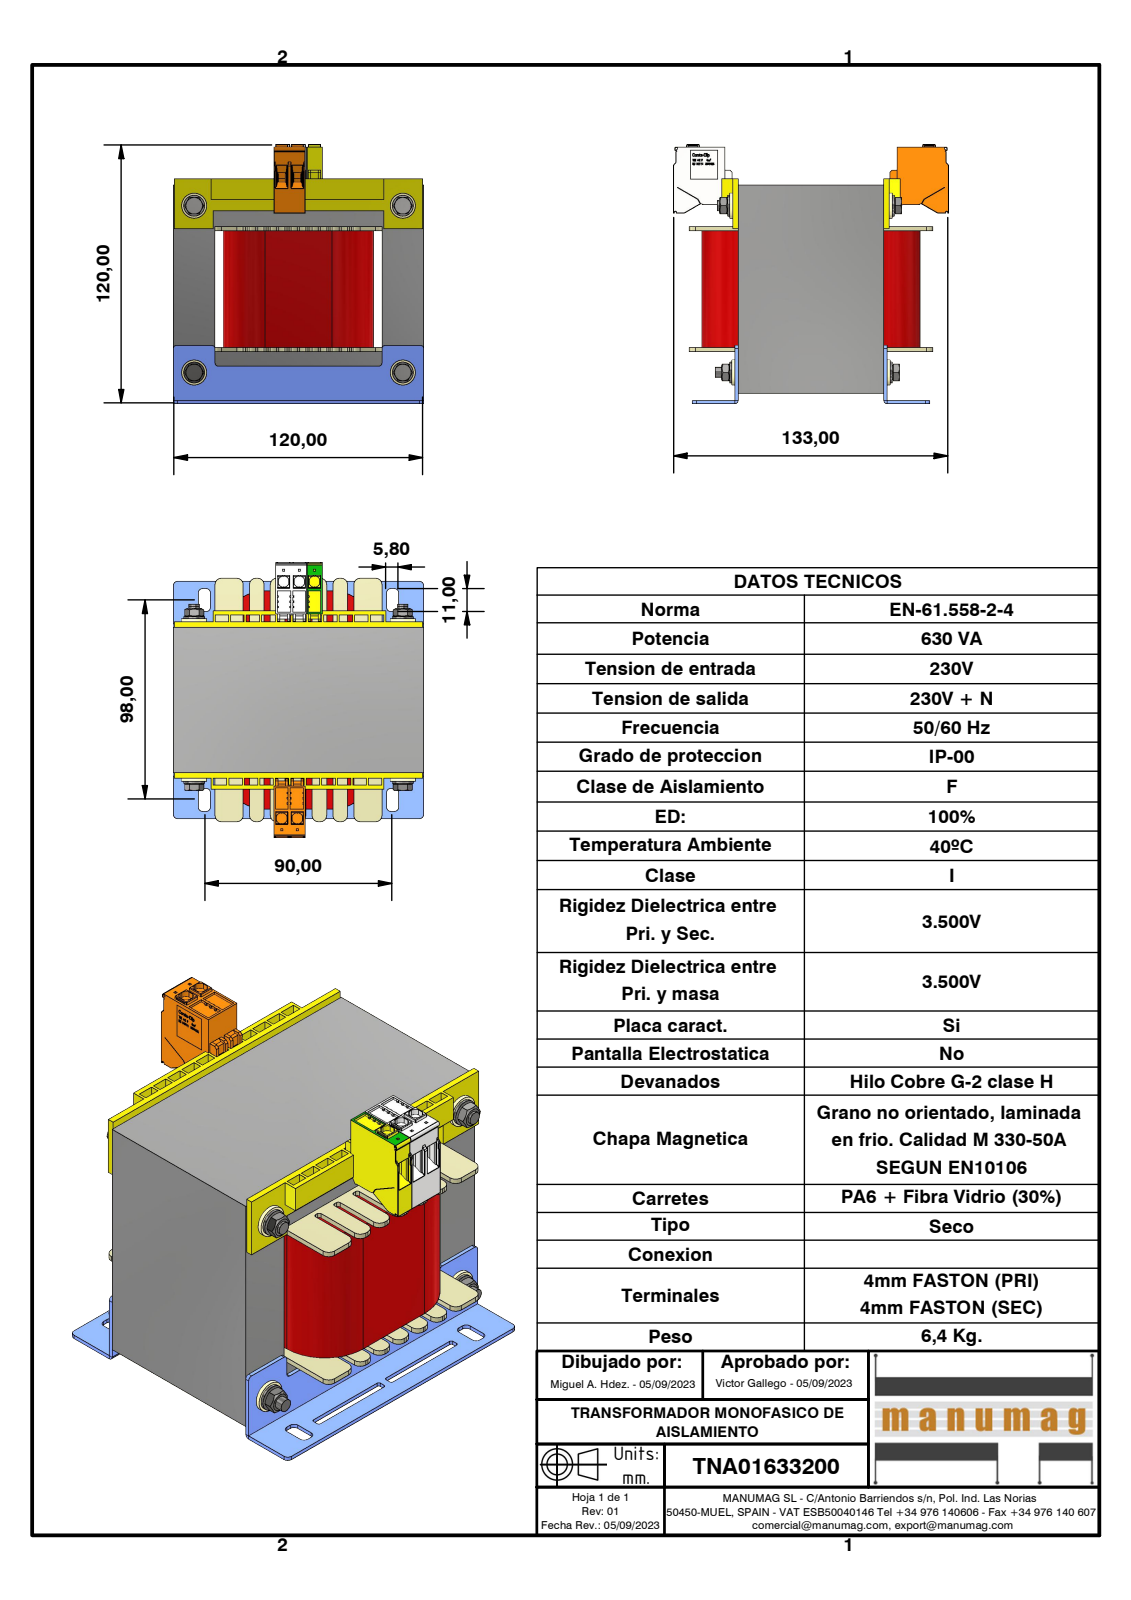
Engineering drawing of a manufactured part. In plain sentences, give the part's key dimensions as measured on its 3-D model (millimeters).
The part is named "TNA01633200; EI120 x 100 - 70 (Rc40); AF40DIN; EI 120 X 100 - 70 (+8 more)". Its 3-D file was written by "Autodesk Inventor 2023 (AUTOMOTIVE_DESIGN)". It is 33 solids with 5387 faces: 4385 planar, 698 cylindrical and 304 other. Overall it measures 132.3 by 124.5 by 120 millimeters. Its volume is 991 420 cubic millimeters and its surface area 192 348 square millimeters. Round holes: 4 of diameter 4.13, 4 of diameter 5, 4 of diameter 5.3, 4 of diameter 6.6, 2 of diameter 6.8. Round bosses or shafts: 4 of diameter 12, 4 of diameter 10, 4 of diameter 6.7, 4 of diameter 5.9, 4 of diameter 4.57. Partial cylindrical surfaces (rounded edges, fillets, slot ends): 216 of radius 0.15, 70 of radius 0.2, 32 of radius 1, 28 of radius 3, 20 of radius 2, 18 of radius 0.5, 18 of radius 0.8, 12 of radius 0.3. The main face-to-face distances are 80, 20, 40, 60, 100, 70, 1.5, 16, 56, 4. The hole center spacings are 80, 100, 128.06.
